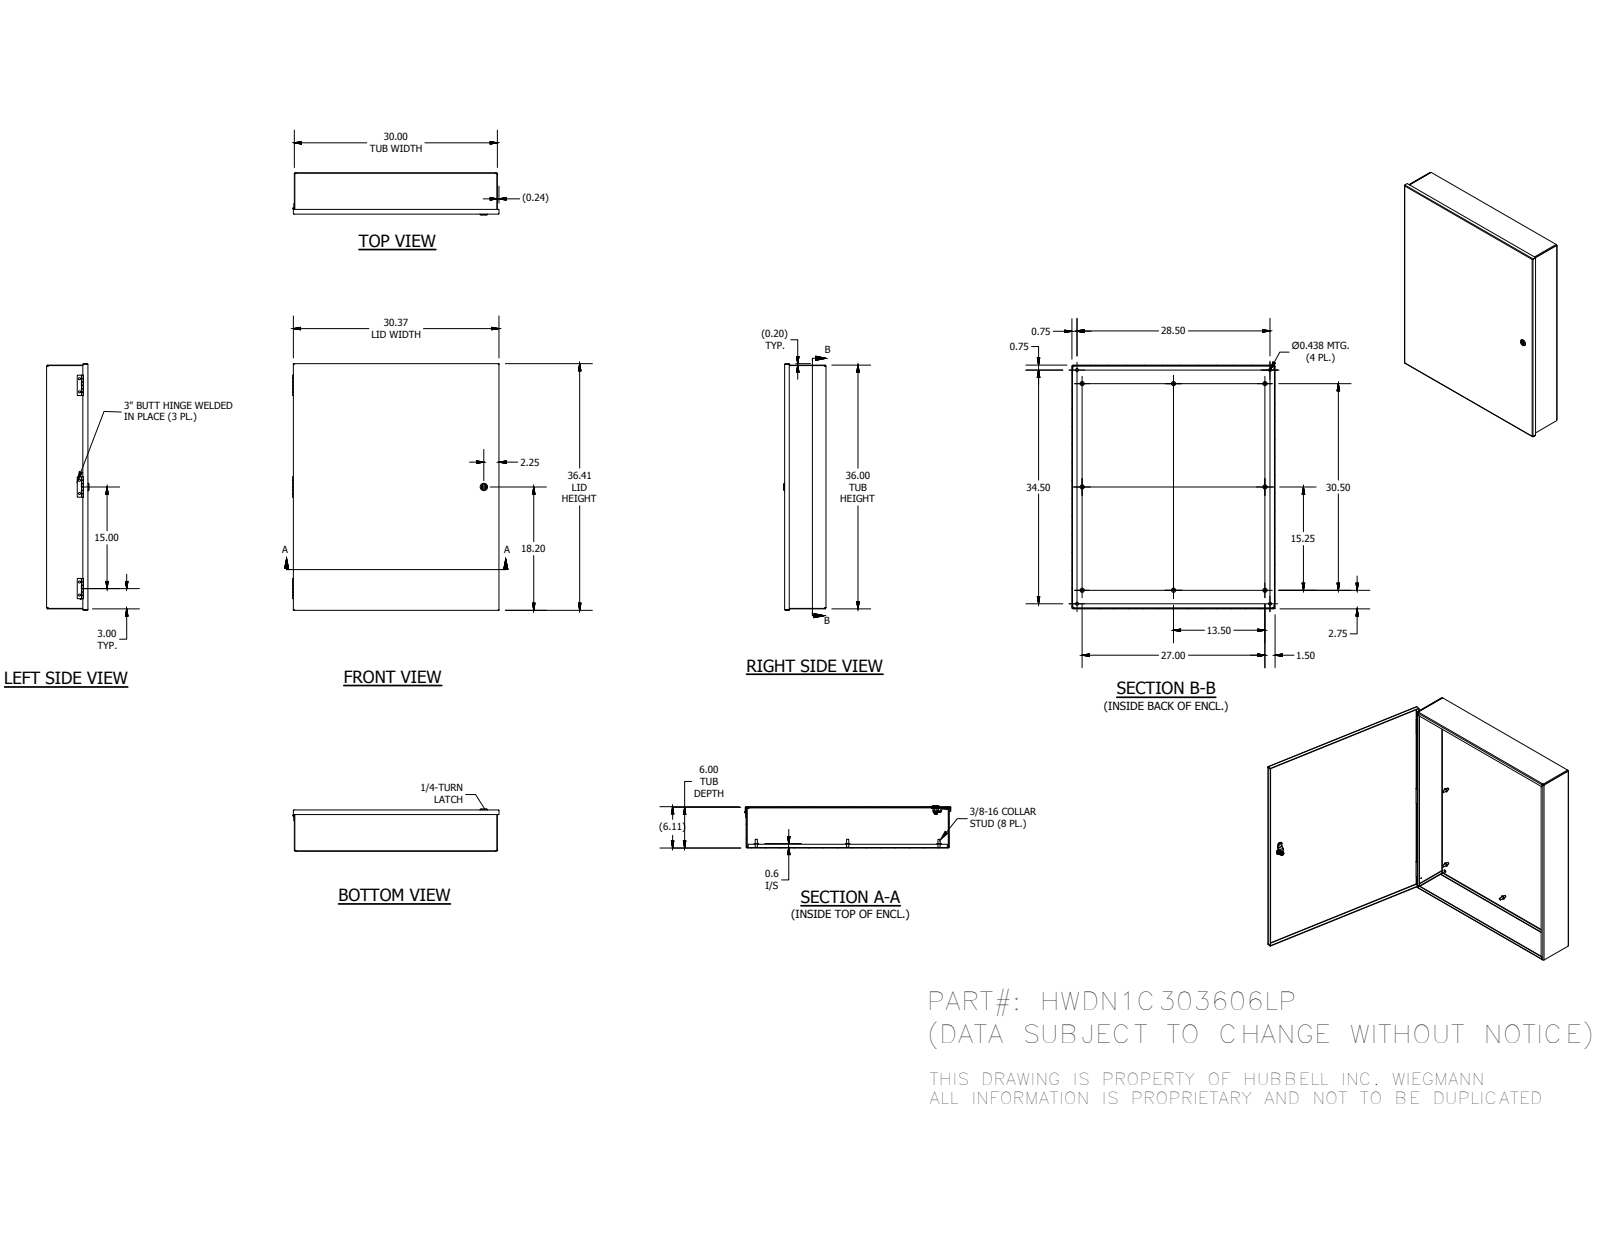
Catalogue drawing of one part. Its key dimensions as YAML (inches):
part_name: "N1C303606LPBLR; N1C3006LPTB; N1C3036LPLID; 1000-101-GPF_GPD (+8 more)"
step_written_by: "Autodesk Inventor 2016 (AUTOMOTIVE_DESIGN)"
units: inches
bodies: {solids: 28, faces: 796, planar: 484, cylindrical: 239, other: 73}
overall_size: [36.406, 30.489, 7.013]
volume: 241.8
surface_area: 6563
round_holes:
  - {diameter: 0.313, count: 6}
  - {diameter: 0.437, count: 4}
  - {diameter: 0.12, count: 1}
  - {diameter: 0.13, count: 1}
  - {diameter: 0.197, count: 1}
  - {diameter: 0.315, count: 1}
  - {diameter: 0.394, count: 1}
  - {diameter: 0.402, count: 1}
  - {diameter: 0.634, count: 1}
  - {diameter: 0.802, count: 1}
round_bosses_or_shafts:
  - {diameter: 0.625, count: 8}
  - {diameter: 0.33, count: 8}
  - {diameter: 1.102, count: 1}
  - {diameter: 1.063, count: 1}
  - {diameter: 0.906, count: 1}
  - {diameter: 0.78, count: 1}
  - {diameter: 0.622, count: 1}
  - {diameter: 0.598, count: 1}
partial_cylinders:
  - {radius: 0.012, count: 30}
  - {radius: 0.063, count: 12}
  - {radius: 0.137, count: 12}
  - {radius: 0.02, count: 10}
  - {radius: 0.031, count: 4}
  - {radius: 0.105, count: 4}
  - {radius: 0.157, count: 4}
  - {radius: 0.016, count: 3}
face_to_face_distances: [0.074, 6.781, 6.707, 6.855, 29.926, 35.926, 29.852, 30, 35.852, 36]
hole_center_spacings: [15, 1.94, 13.06, 16.94, 17.296, 28.5, 30, 32.241]
